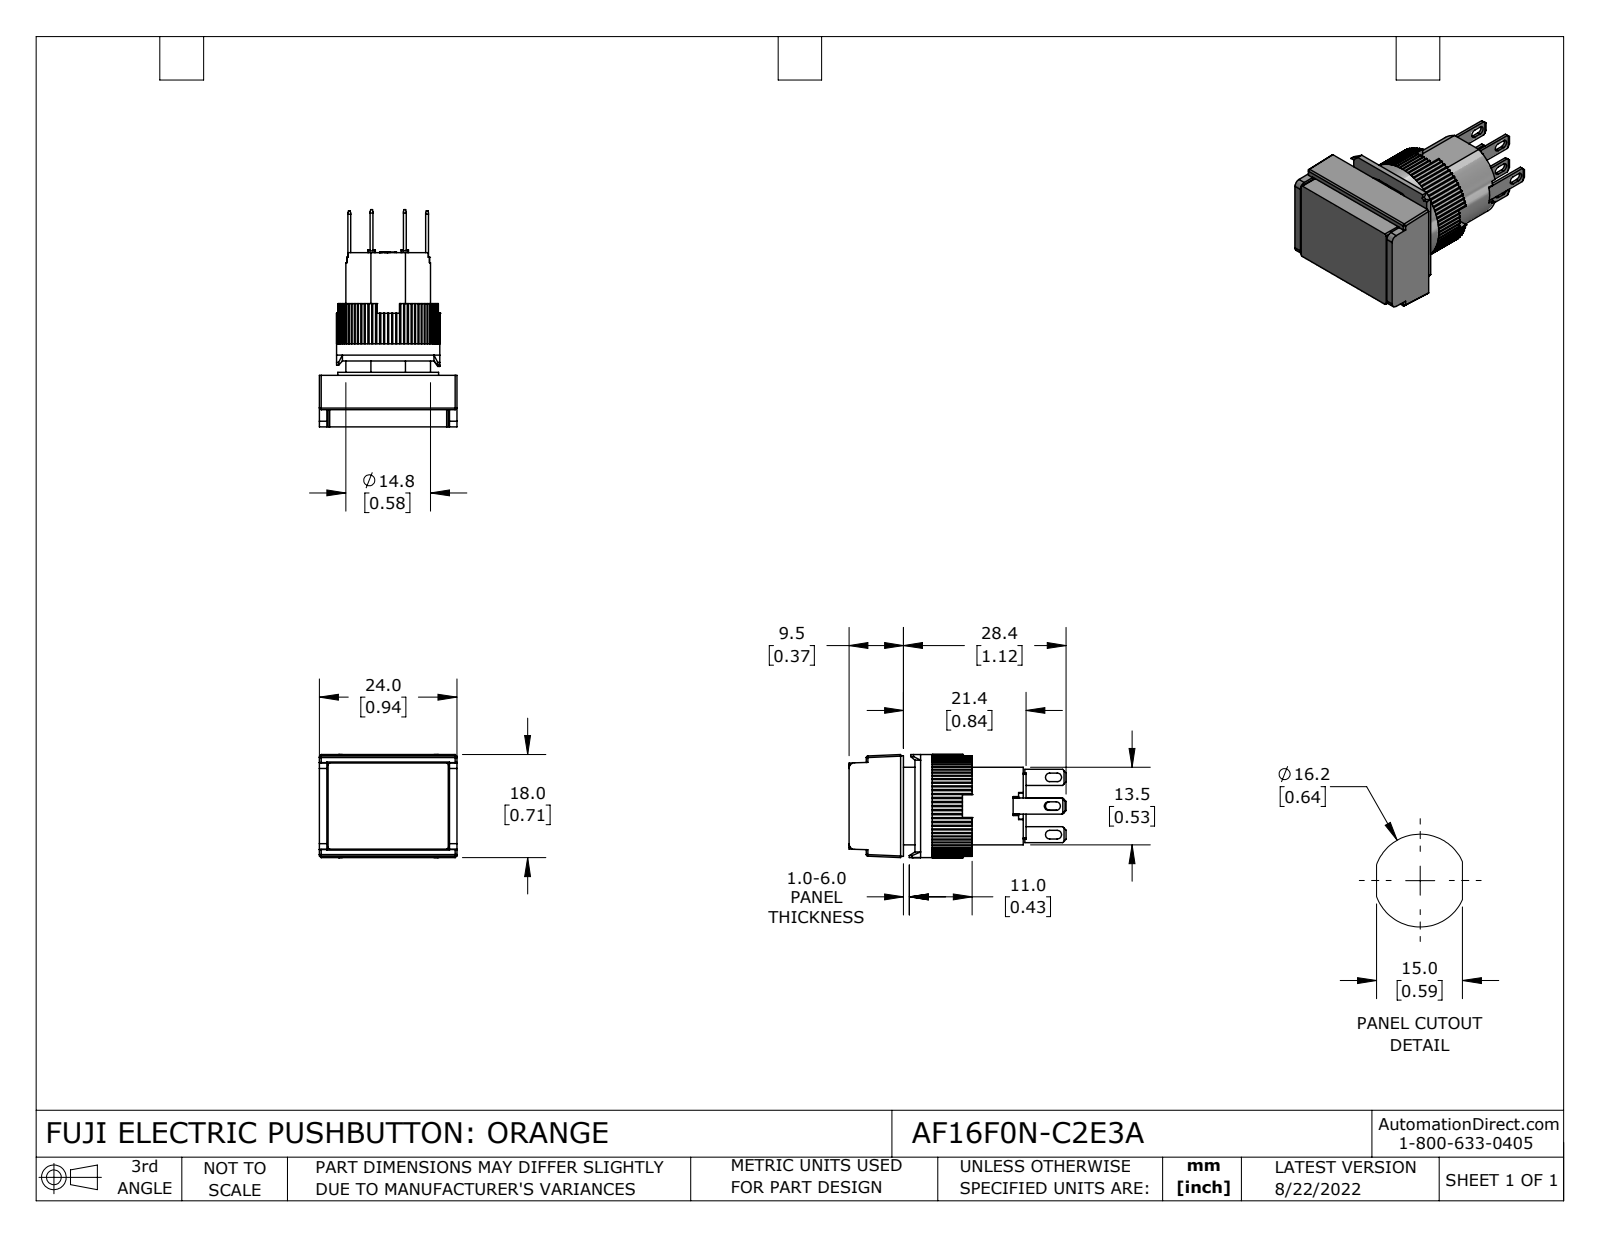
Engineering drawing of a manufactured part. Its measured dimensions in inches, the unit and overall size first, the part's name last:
Units: inches
Overall size (bounding box): 1.492 × 0.945 × 0.709
Round holes (diameter × count): ⌀0.543 ×1, ⌀0.583 ×1
Round bosses / shafts (diameter × count): ⌀0.709 ×1, ⌀0.693 ×1
Partial cylindrical surfaces — rounded edges, fillets, slot ends (radius × count): R0.01 ×80, R0.008 ×12, R0.03 ×8, R0.012 ×6, R0.039 ×2
Main face-to-face distances: 0.213, 0.354, 0.142, 0.35, 0.492, 0.138, 0.02, 0.843, 0.059, 0.453
Volume: 0.444 in³ · Surface area: 9.306 in²
Bodies: 14 solids, 843 faces (656 planar, 183 cylindrical, 4 other)
Part name (STEP PRODUCT): AF16F0N-C2E3A
STEP written by: SolidWorks 2021 (CONFIG_CONTROL_DESIGN)
